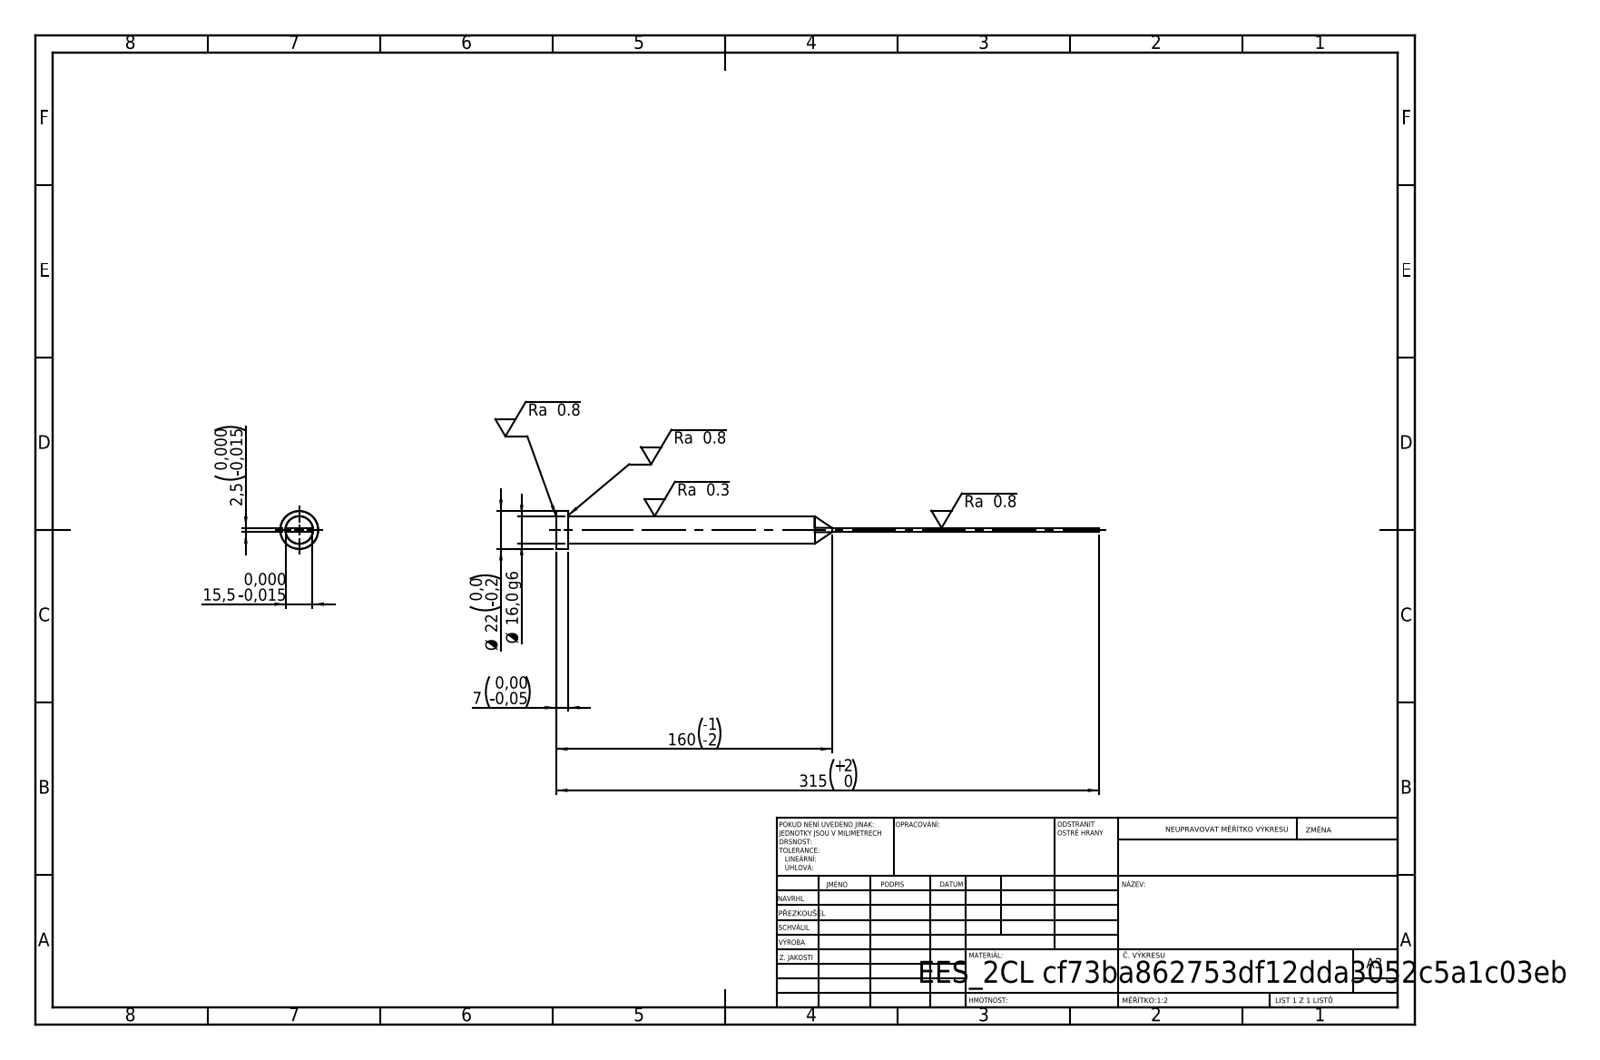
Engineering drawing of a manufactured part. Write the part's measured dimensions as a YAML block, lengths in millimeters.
step_written_by: "SolidWorks 2019 (CONFIG_CONTROL_DESIGN)"
units: millimeters
bodies: {solids: 1, faces: 15, planar: 7, cylindrical: 4, other: 4}
overall_size: [315, 22, 22]
volume: 38556
surface_area: 14300
round_bosses_or_shafts:
  - {diameter: 22, count: 1}
  - {diameter: 16, count: 1}
face_to_face_distances: [2.5, 15.5, 7, 315, 308]
